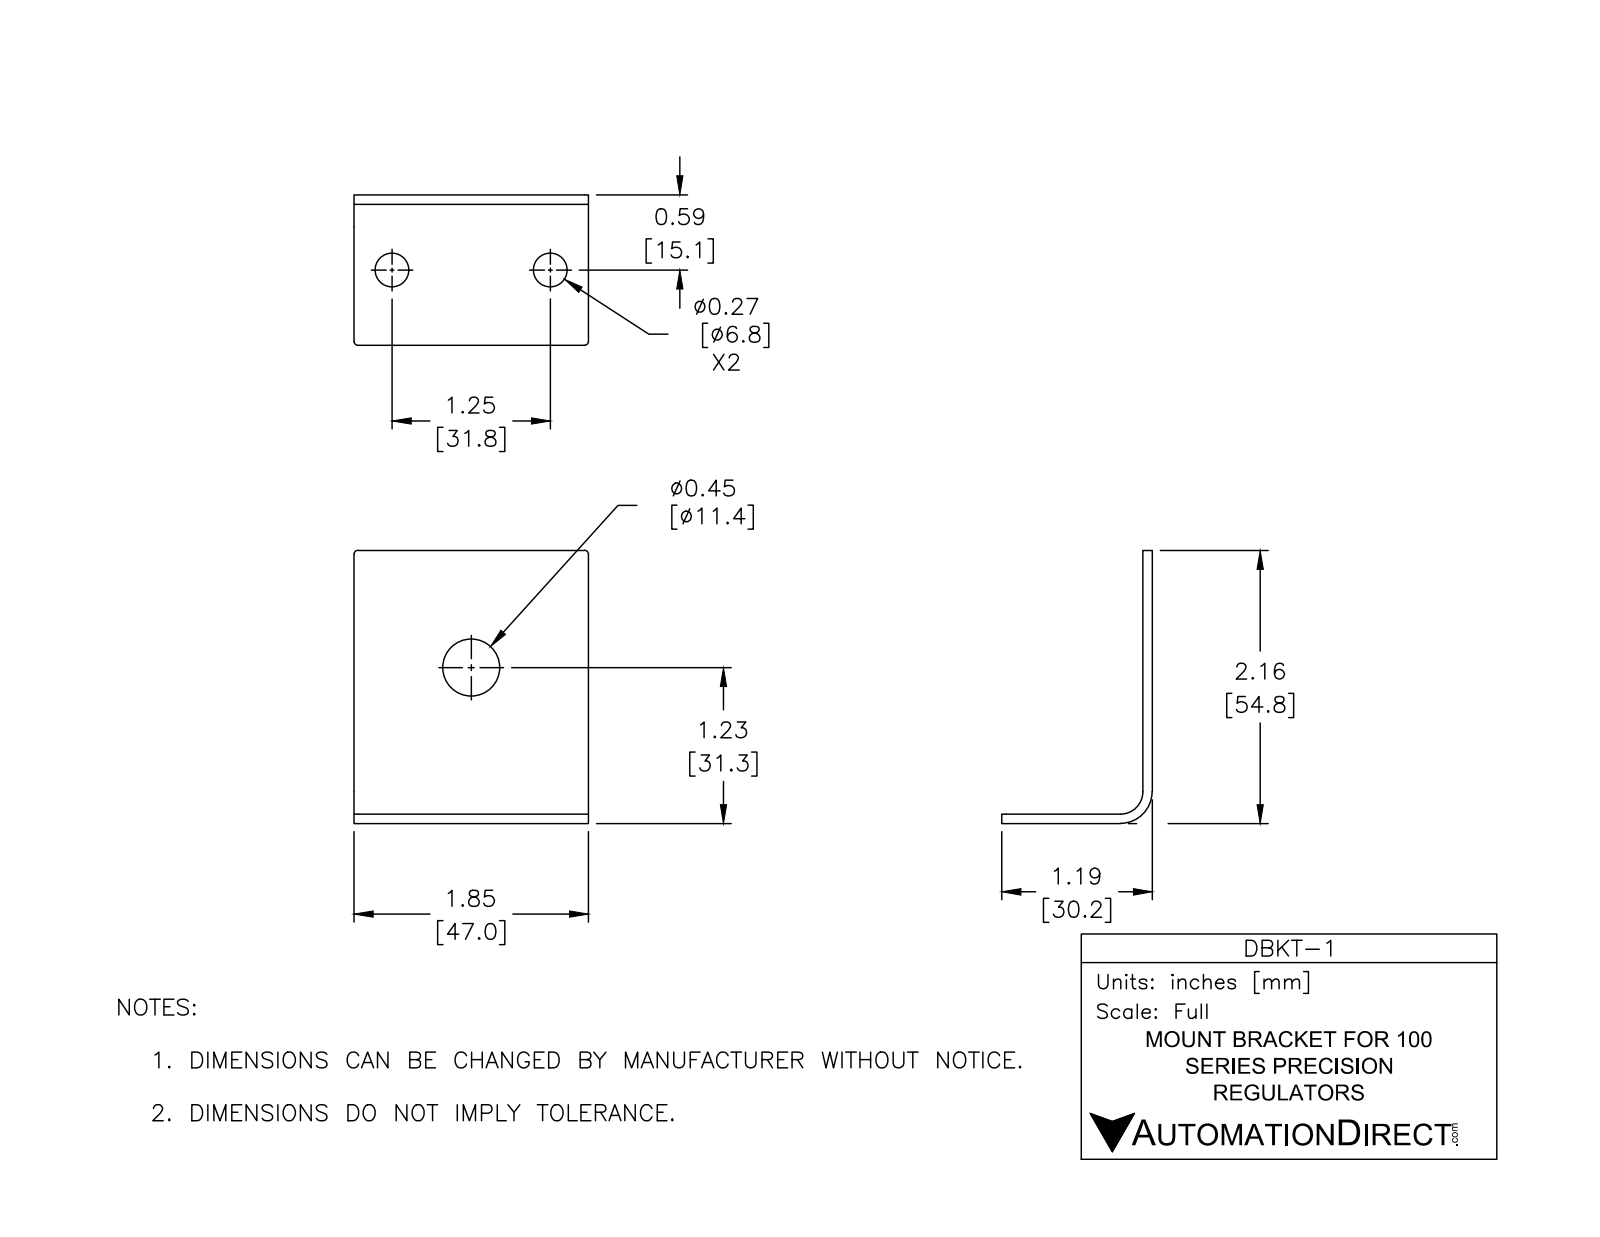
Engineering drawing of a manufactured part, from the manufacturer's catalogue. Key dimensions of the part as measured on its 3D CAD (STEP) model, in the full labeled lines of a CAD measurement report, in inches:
Part name (STEP PRODUCT): 707045
STEP written by: Autodesk Inventor 2014 (AUTOMOTIVE_DESIGN)
Units: inches
Bodies: 1 solid, 17 faces (8 planar, 9 cylindrical, 0 other)
Overall size (bounding box): 2.156 × 1.85 × 1.188
Volume: 0.419 in³ · Surface area: 12.19 in²
Round holes (diameter × count): ⌀0.266 ×2, ⌀0.45 ×1
Partial cylindrical surfaces — rounded edges, fillets, slot ends (radius × count): R0.031 ×4, R0.177 ×1, R0.25 ×1
Main face-to-face distances: 0.075, 0.074, 1.85, 2.156, 2.081, 1.188, 1.113
Hole centre spacings: 1.25
